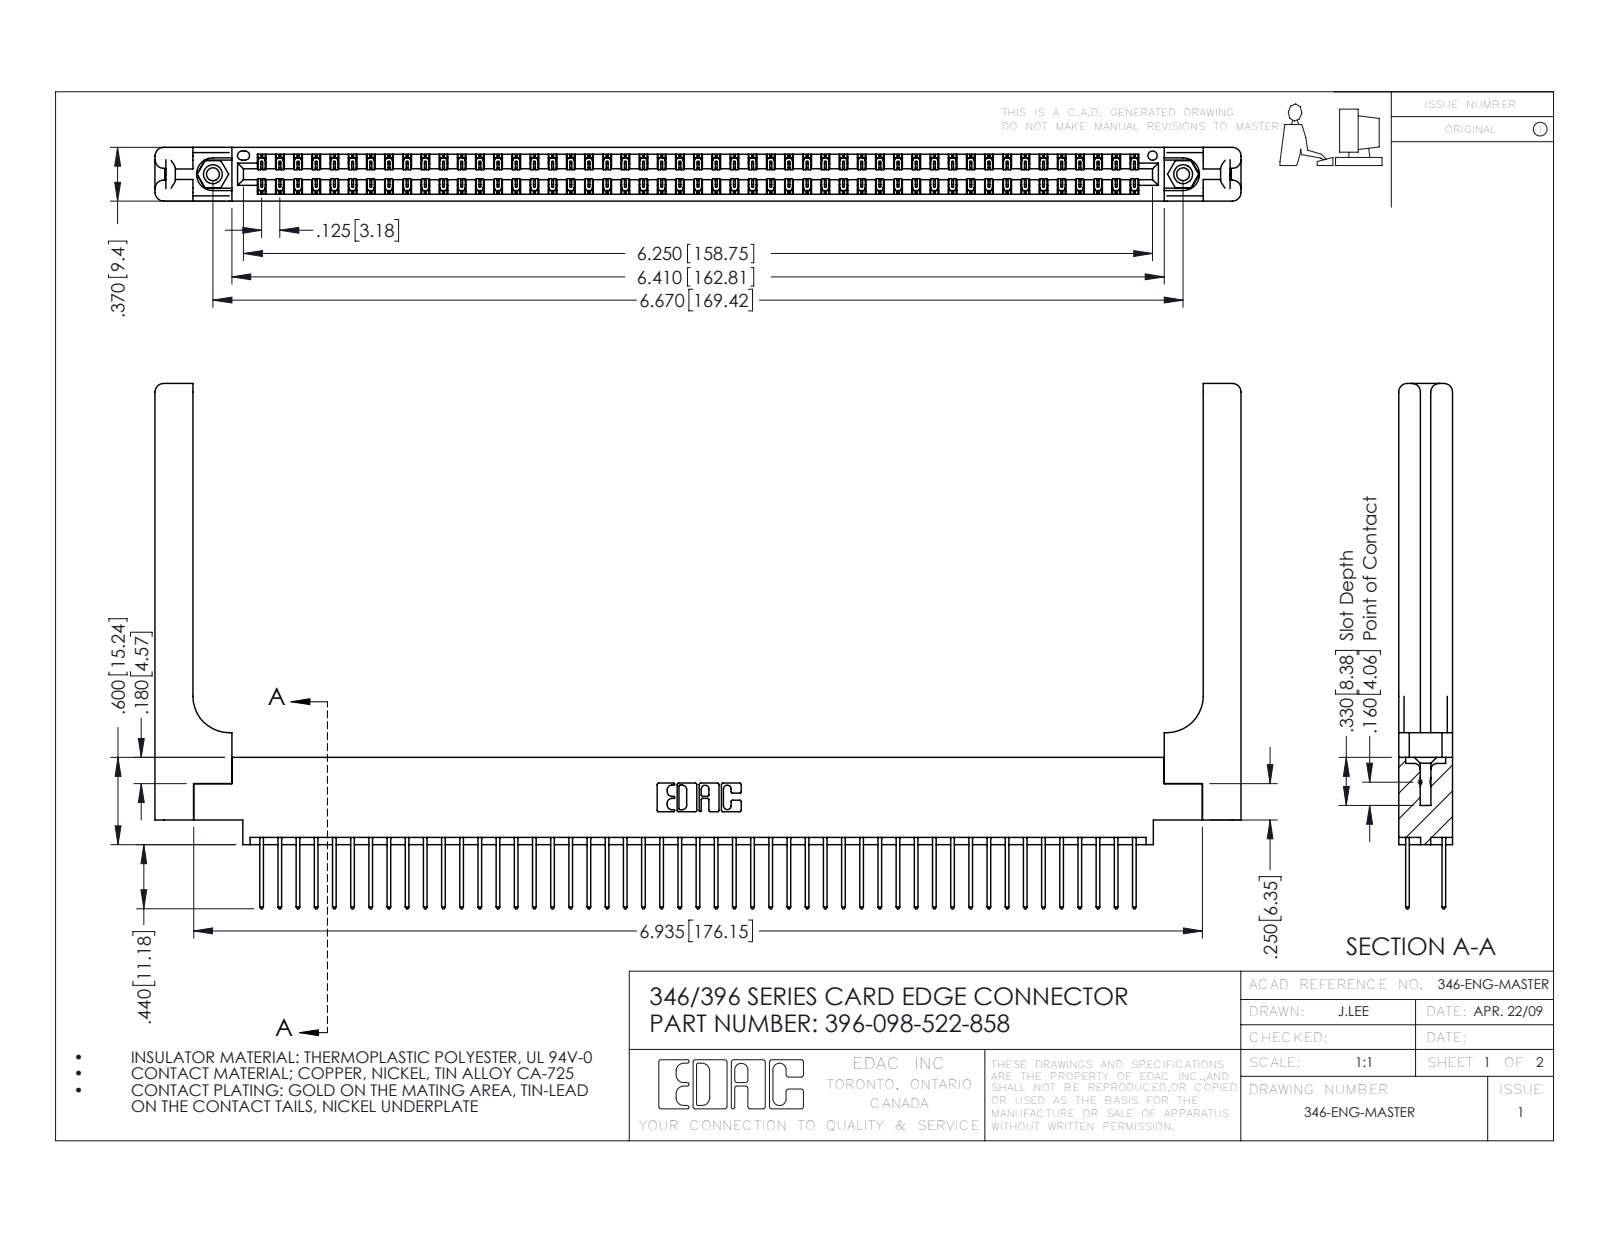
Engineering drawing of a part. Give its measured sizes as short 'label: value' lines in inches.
name: 345-250-001_345-250-001-102; 396-098-522-858; 346 Part_0.170 Offset - 0.156 Dia-TH; 345-292-001_345-293-122 (+1 more)
written by: SolidWorks 2016 (CONFIG_CONTROL_DESIGN)
unit: in
bodies: 103 solids, 5478 faces (3658 planar, 1760 cylindrical, 60 other)
size: 7.466 × 3.61 × 0.37
volume: 1.595 in³; area: 49.68 in²
holes: 2× ⌀0.089, 2× ⌀0.125, 2× ⌀0.156, 1× ⌀0.064
bosses: 2× ⌀0.155
rounds: 147× R0.006, 98× R0.01, 22× R0.01, 16× R0.06, 6× R0.007, 6× R0.031, 3× R0.026, 2× R0.014
face distances: 0.048, 0.322, 0.37, 0.072, 0.25, 0.025, 0.298, 0.148, 0.15, 0.275
hole spacings: 0.246, 6.461, 6.67
